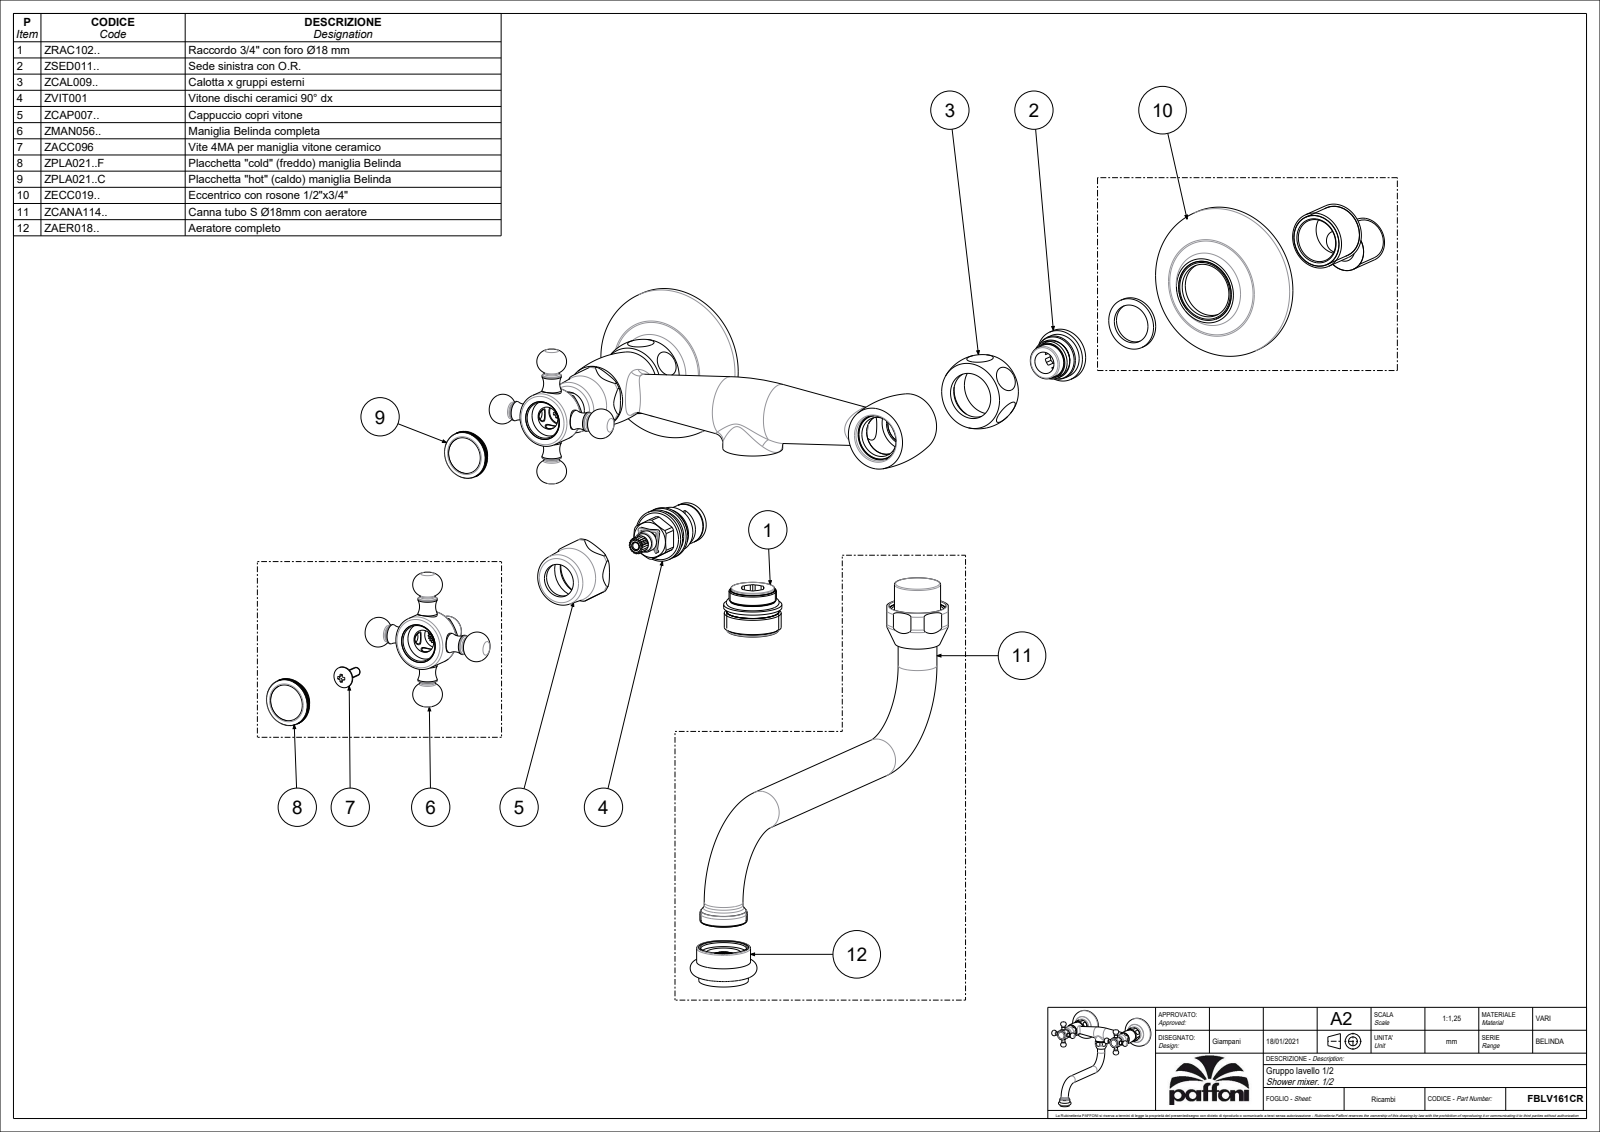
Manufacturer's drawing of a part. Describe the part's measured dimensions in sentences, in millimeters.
The part is named "FBLV161CR". Its 3-D file was written by "CREO PARAMETRIC BY PTC INC, 2020044 (CONFIG_CONTROL_DESIGN)". It is 3 solids with 1222 faces: 516 planar, 368 cylindrical and 338 other. Overall it measures 251.3 by 220 by 178.8 millimeters. Its volume is 215 150 cubic millimeters and its surface area 97 841 square millimeters. Round holes: 2 of diameter 16.5, 2 of diameter 18.6, 2 of diameter 19, 2 of diameter 21.5, 2 of diameter 25, 2 of diameter 68, 1 of diameter 12.6, 1 of diameter 13.8, 1 of diameter 16.1, 1 of diameter 16.6, 1 of diameter 18.2, 1 of diameter 18.7. Round bosses or shafts: 3 of diameter 18, 3 of diameter 14, 3 of diameter 9, 3 of diameter 7, 2 of diameter 70, 2 of diameter 28.14, 2 of diameter 13, 1 of diameter 27.8. Partial cylindrical surfaces (rounded edges, fillets, slot ends): 2 of radius 11, 1 of radius 5.25, 1 of radius 15. The main face-to-face distances are 17.5, 18, 50.69, 33.19, 86, 0.5, 68.5, 35.31, 7, 25. The hole center spacings are 150.
